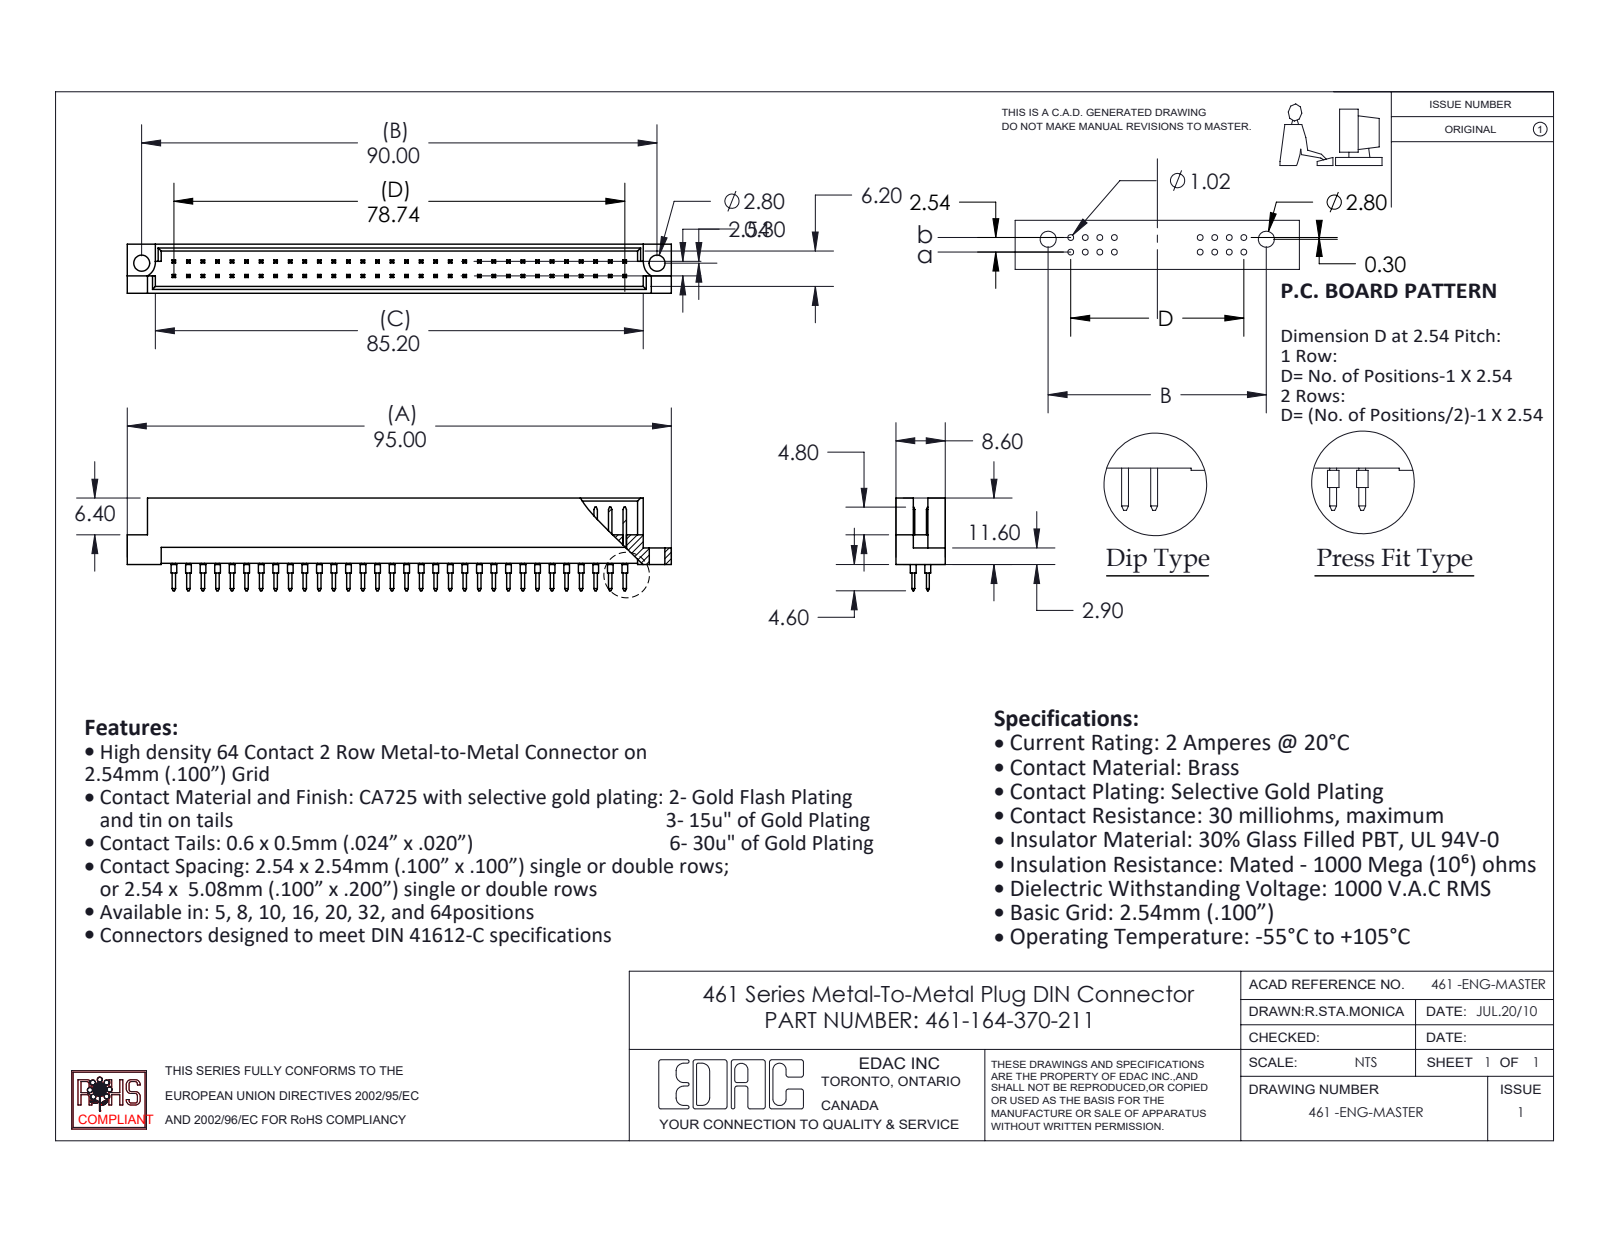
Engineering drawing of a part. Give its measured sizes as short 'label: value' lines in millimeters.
name: 461-164-370-211; 461 Part_64; 461-290_70
written by: SolidWorks 2020 (CONFIG_CONTROL_DESIGN)
unit: mm
bodies: 65 solids, 1713 faces (1578 planar, 135 cylindrical, 0 other)
size: 95 × 16.2 × 8.6
volume: 4 976 mm³; area: 7 855 mm²
holes: 2× ⌀2.8
bosses: 64× ⌀1
rounds: 2× R2.8
face distances: 1.2, 7.4, 8.6, 2.54, 6.2, 3.28, 5.32, 2.08, 4.12, 2.78
hole spacings: 90
